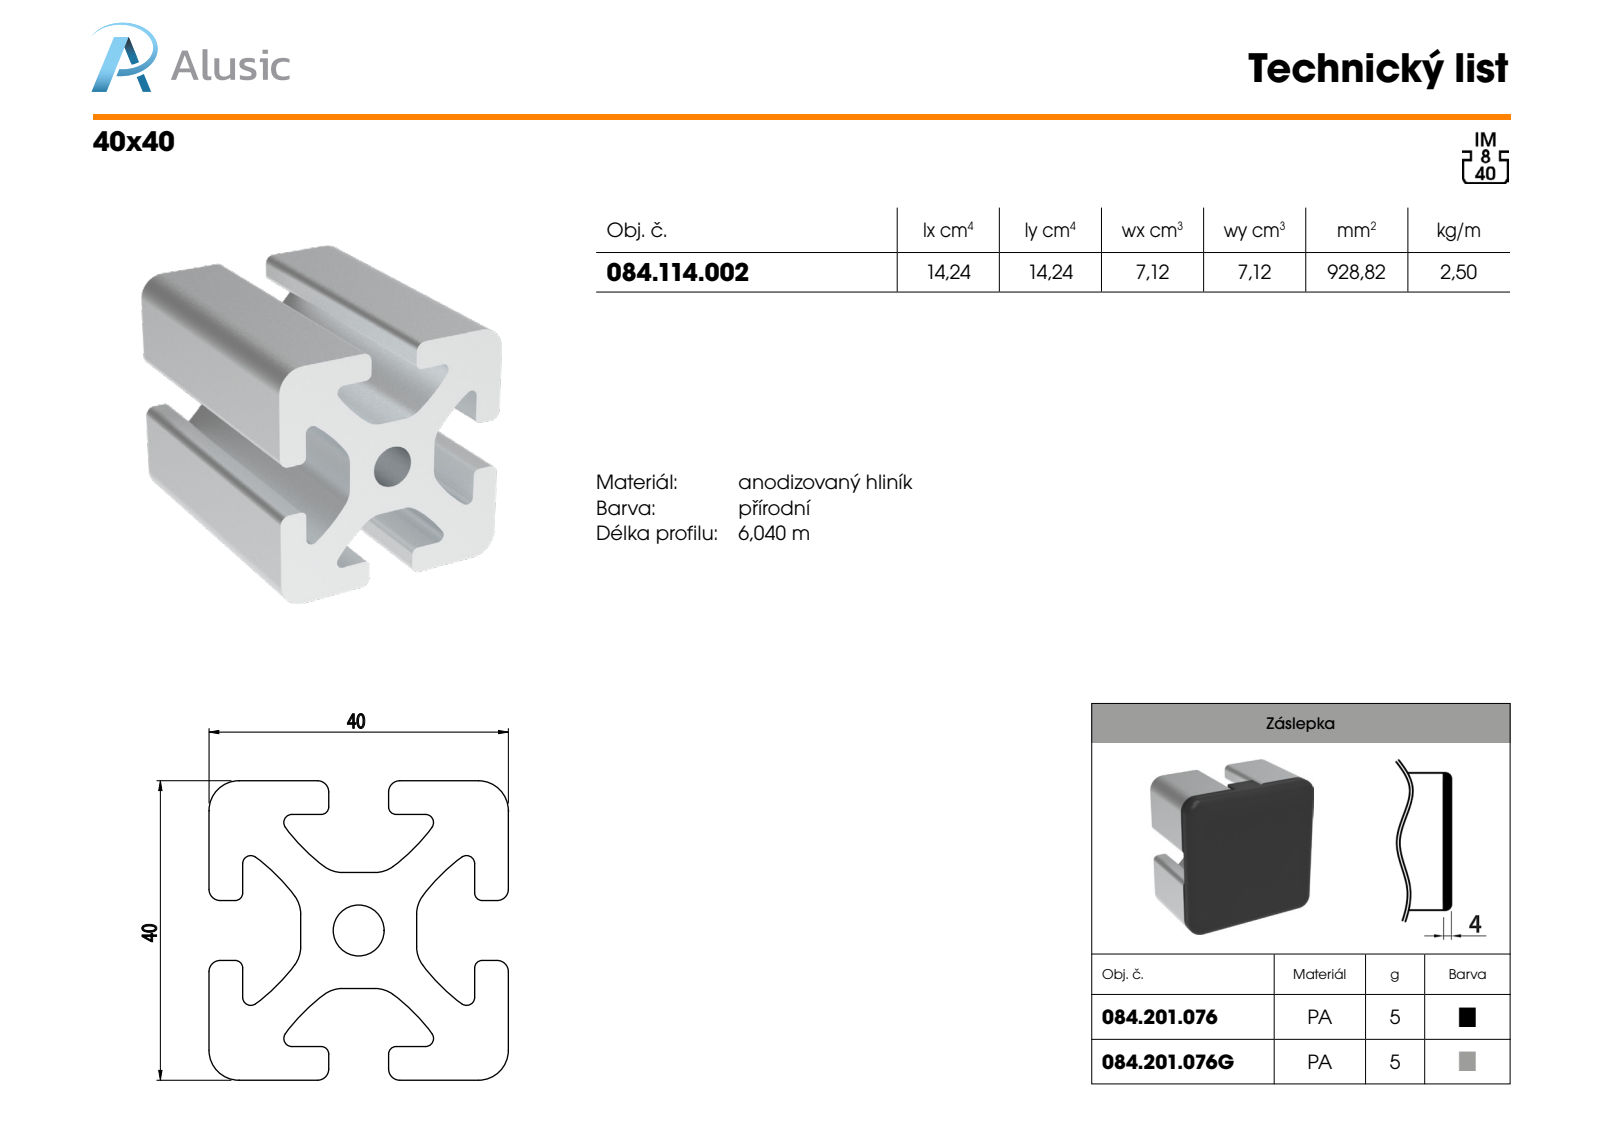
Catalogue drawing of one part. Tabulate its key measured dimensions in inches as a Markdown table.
| quantity | value |
| --- | --- |
| part name | 084.114.002. |
| STEP written by | SolidWorks 2018 (AUTOMOTIVE_DESIGN) |
| units | inches |
| bodies | 1 solid, 78 faces (30 planar, 48 cylindrical, 0 other) |
| overall size | 3.937 × 1.575 × 1.575 |
| volume | 5.657 in³ |
| surface area | 53.23 in² |
| round holes (diameter × count) | 0.268 × 1 |
| partial cylindrical surfaces (radius × count) | 0.157 × 12, 0.039 × 8, 0.043 × 8, 0.059 × 8, 0.984 × 8 |
| main face-to-face distances | 1.575, 0.177, 1.398, 0.482, 1.093, 0.305, 0.915, 0.628, 0.451, 0.146 |
